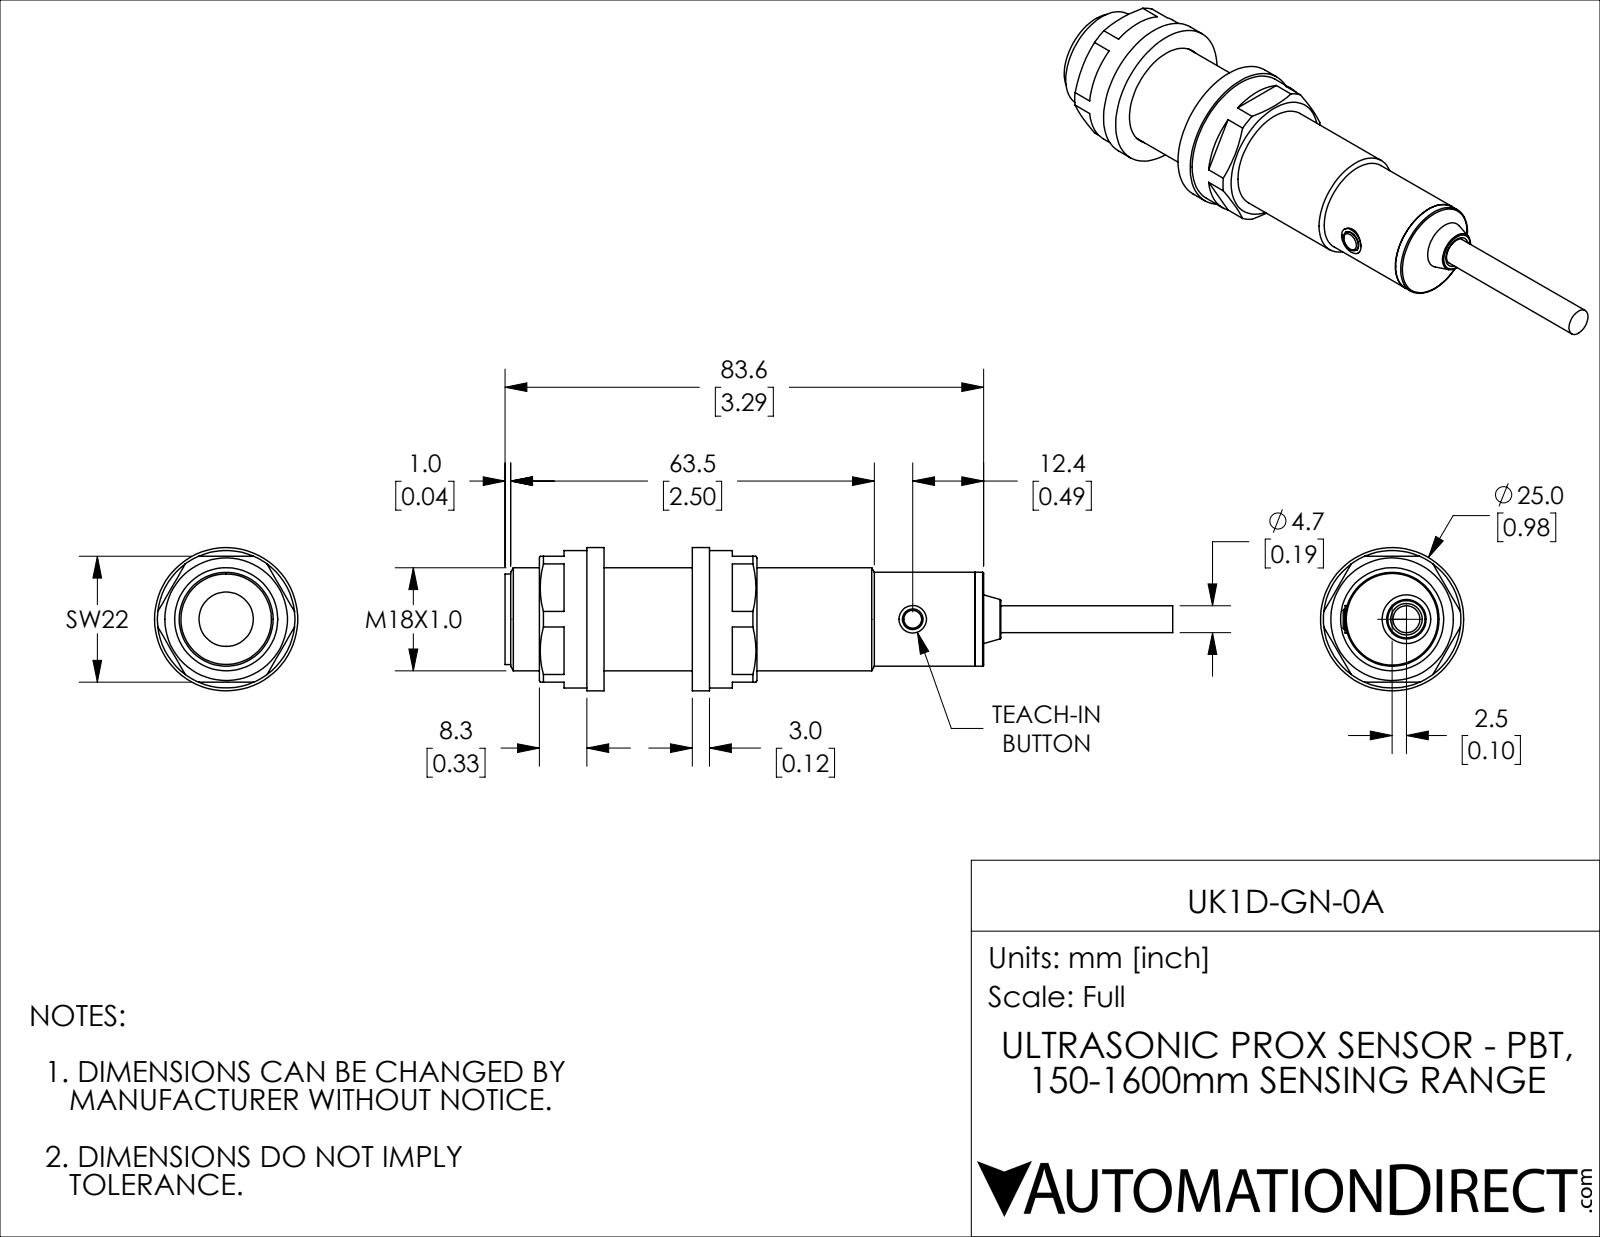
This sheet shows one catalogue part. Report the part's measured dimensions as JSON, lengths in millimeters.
{"part_name": "UK1D-GN-0A", "step_written_by": "SolidWorks 2018 (AUTOMOTIVE_DESIGN)", "units": "millimeters", "bodies": {"solids": 10, "faces": 107, "planar": 49, "cylindrical": 40, "other": 18}, "overall_size": [116.6, 25, 25], "volume_mm3": 25220, "surface_area_mm2": 11419, "round_holes": [[4.7, 2], [3.6, 1], [9.5, 1], [18, 1], [18.2, 1]], "round_bosses_or_shafts": [[25, 1], [24, 1], [16.4, 1], [15.8, 1], [5.4, 1], [4.8, 1]], "face_to_face_distances": [3, 18.4, 21.4, 67.8, 46.4, 13.3, 34.7, 81.1, 16.3, 64.8], "hole_center_spacings": [2.5]}
